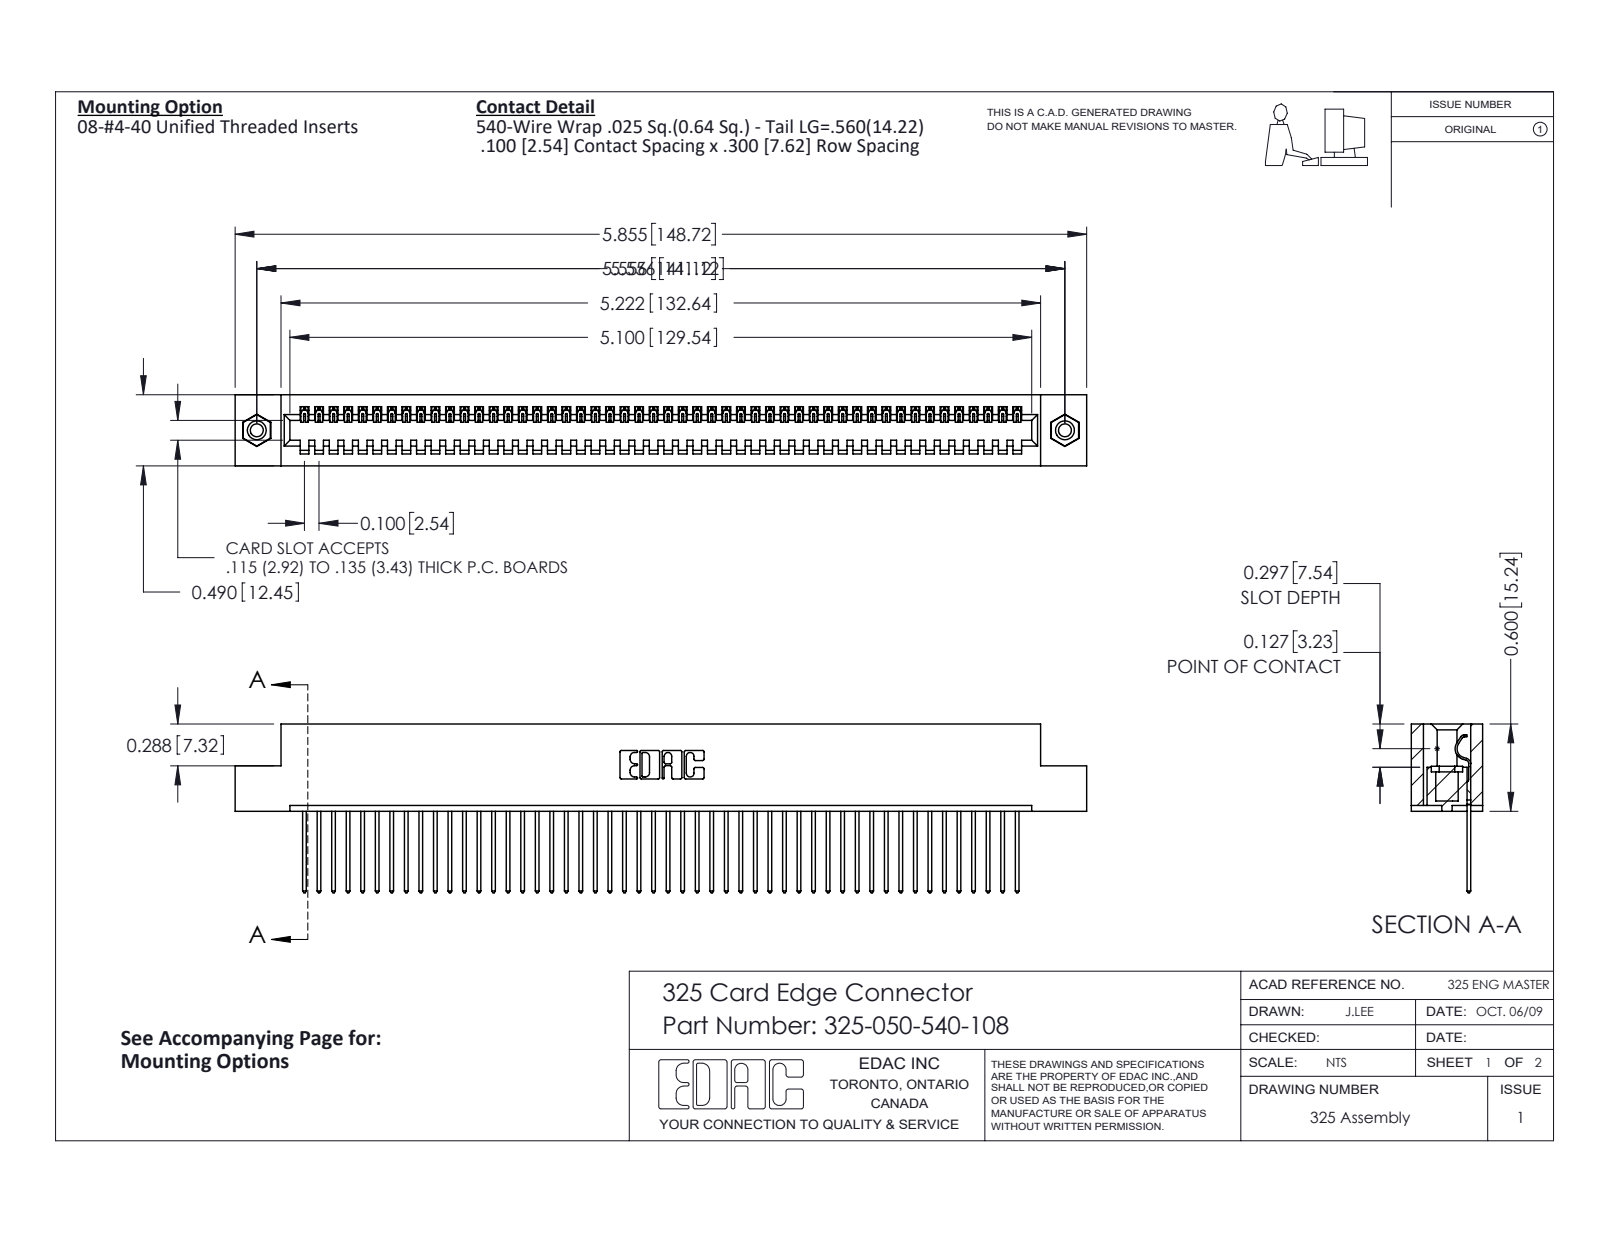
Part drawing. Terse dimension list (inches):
name: 325 Part_TI; 325-292-001_325-293-140; 325-050-540-108; 345-250-001_345-250-003-102
written by: SolidWorks 2016 (CONFIG_CONTROL_DESIGN)
unit: in
bodies: 53 solids, 3074 faces (2202 planar, 856 cylindrical, 16 other)
size: 5.855 × 1.16 × 0.49
volume: 1.16 in³; area: 33.19 in²
holes: 2× ⌀0.089, 2× ⌀0.125, 2× ⌀0.16
bosses: 2× ⌀0.155
rounds: 100× R0.006, 100× R0.01, 22× R0.01, 6× R0.007, 6× R0.031, 3× R0.026, 1× R0.014, 1× R0.022
face distances: 0.083, 0.407, 0.49, 0.3, 0.107, 0.383, 0.025, 0.325, 0.56, 0.263
hole spacings: 5.556
